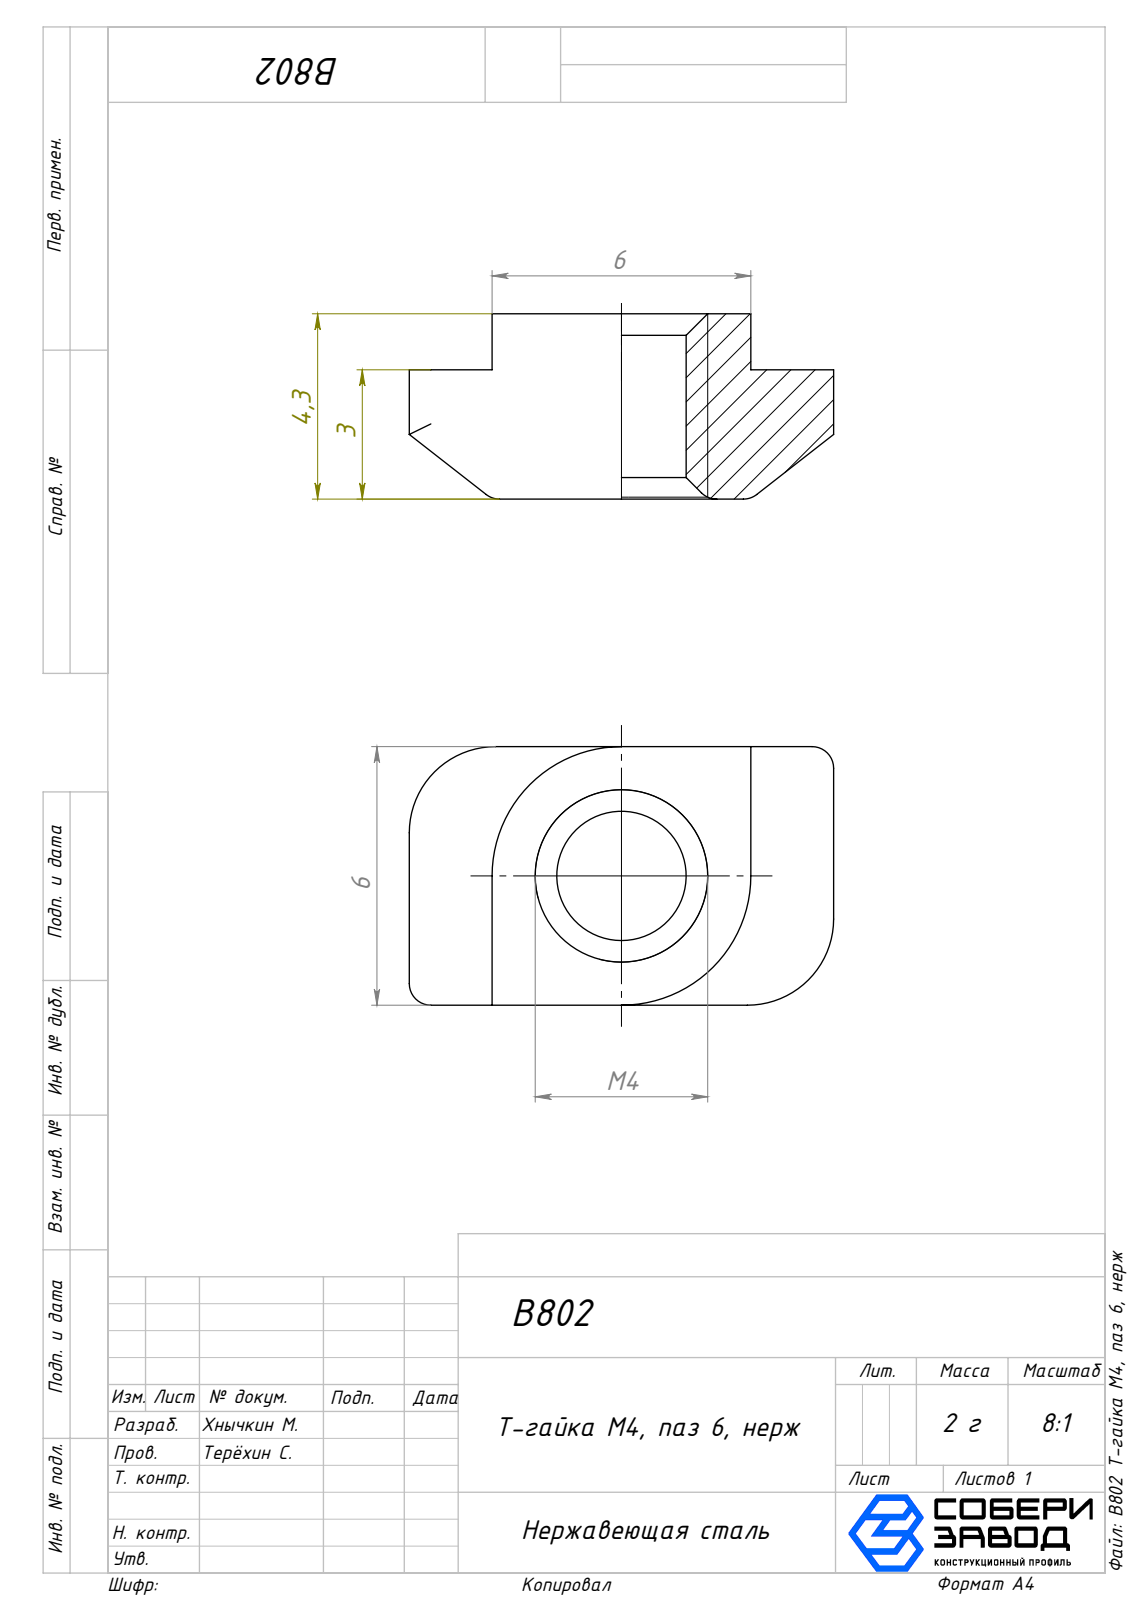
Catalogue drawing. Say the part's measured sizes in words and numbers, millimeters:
The part is named "B802 Т-гайка М4, паз 6, нерж". Its 3-D file was written by "SolidWorks 2025 (AUTOMOTIVE_DESIGN)". It is 1 solid with 38 faces: 12 planar, 16 cylindrical and 10 other. Overall it measures 9.84 by 6 by 4.3 millimeters. Its volume is 161 cubic millimeters and its surface area 230 square millimeters. Round holes: 1 of diameter 3. Partial cylindrical surfaces (rounded edges, fillets, slot ends): 8 of radius 0.5, 4 of radius 2, 1 of radius 3. The main face-to-face distances are 6, 1.3, 3, 4.3, 1.92, 7.92, 9.84.
